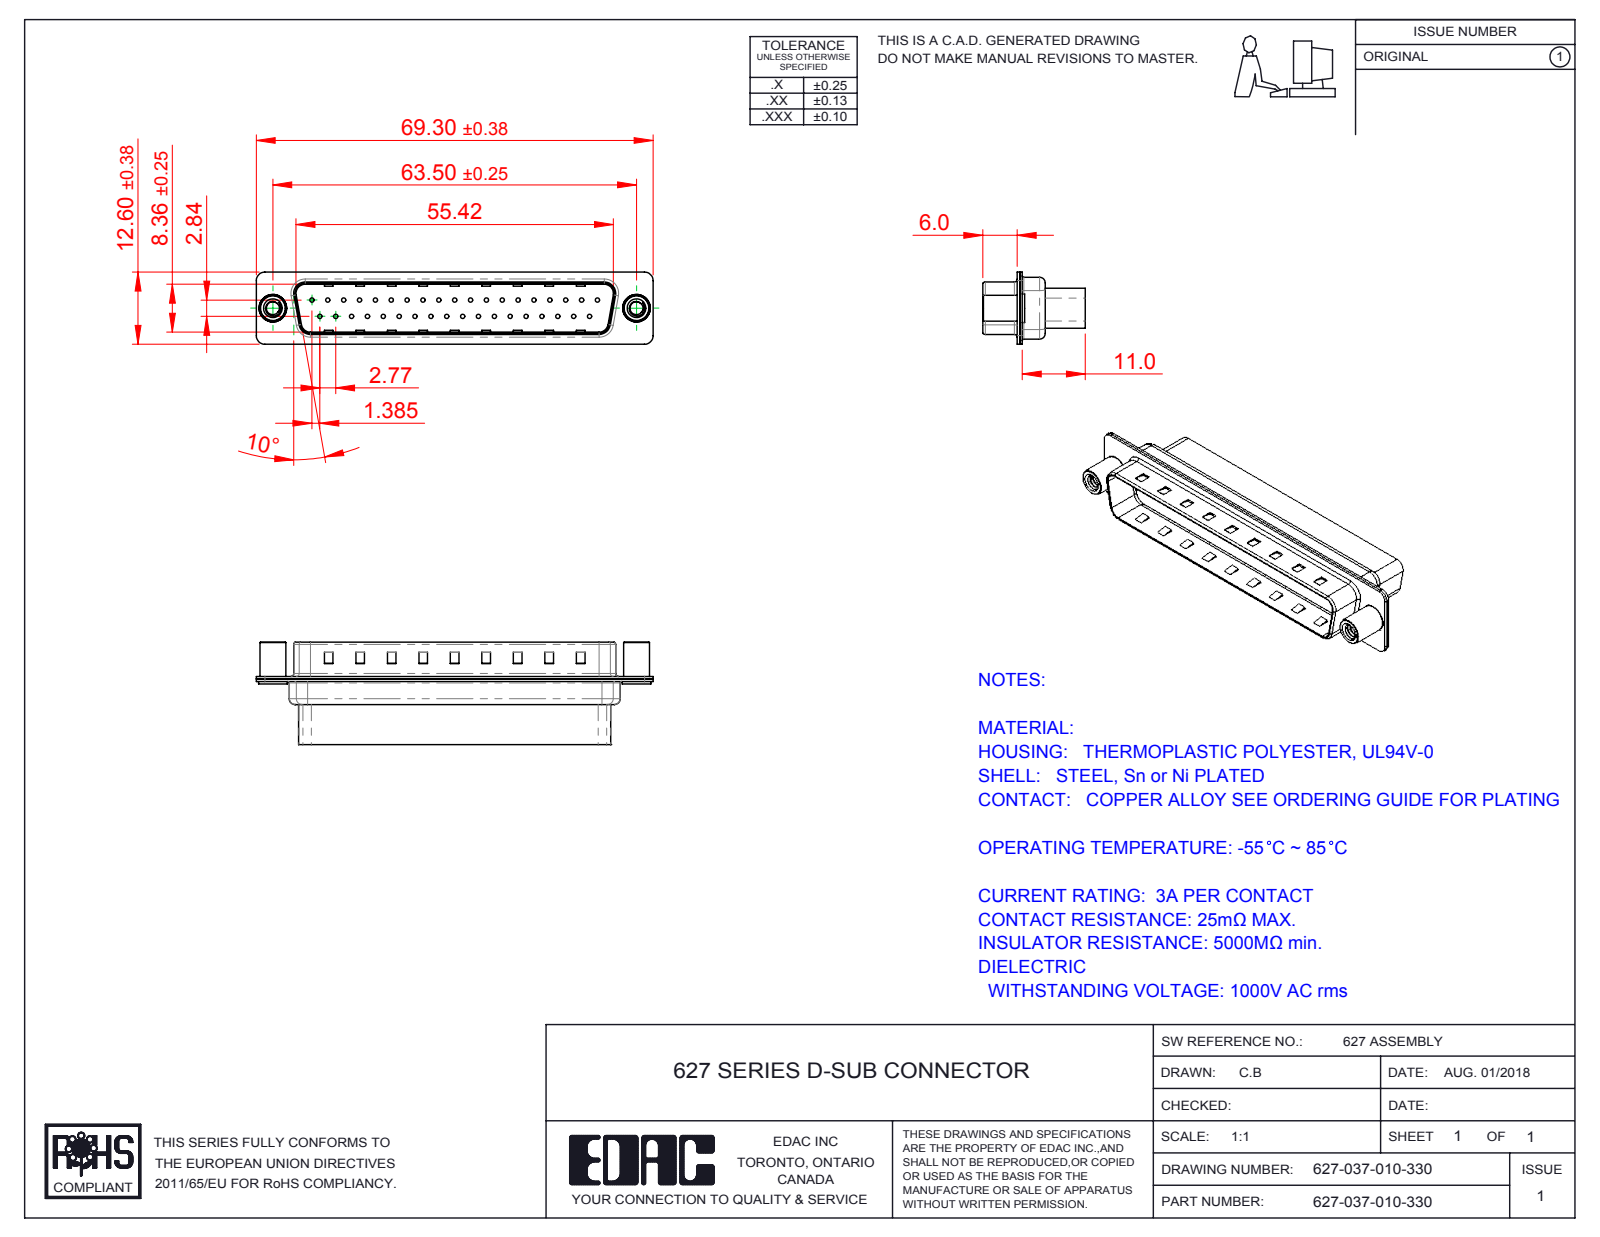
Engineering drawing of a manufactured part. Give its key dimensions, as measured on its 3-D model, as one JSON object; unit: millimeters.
{"part_name": "627 Shell Rear_37 Contacts; 627 4-40 Threaded Standoff; 627 Housing_37 HP; 627-037-010-330 (+1 more)", "step_written_by": "SolidWorks 2016 (CONFIG_CONTROL_DESIGN)", "units": "millimeters", "bodies": {"solids": 5, "faces": 742, "planar": 279, "cylindrical": 391, "other": 72}, "overall_size": [69.3, 17.9, 12.6], "volume_mm3": 5087, "surface_area_mm2": 9232, "round_holes": [[0.75, 37], [1.6, 37], [2, 37], [2.26, 2], [4, 2], [4.8, 2]], "round_bosses_or_shafts": [[5, 2], [4.9, 2], [4.5, 2]], "partial_cylinders_radius": [[1.5, 16], [2, 12], [0.5, 8], [1.6, 8], [0.25, 4], [0.6, 4], [0.65, 4], [0.9, 4]], "face_to_face_distances": [0.4, 0.82, 9.58, 0.68, 7.68, 0.45, 1.08, 8.08, 8.76, 7], "hole_center_spacings": [3.16, 2.77, 5.54, 8.31, 5.04, 10.1, 11.08, 12.78]}
